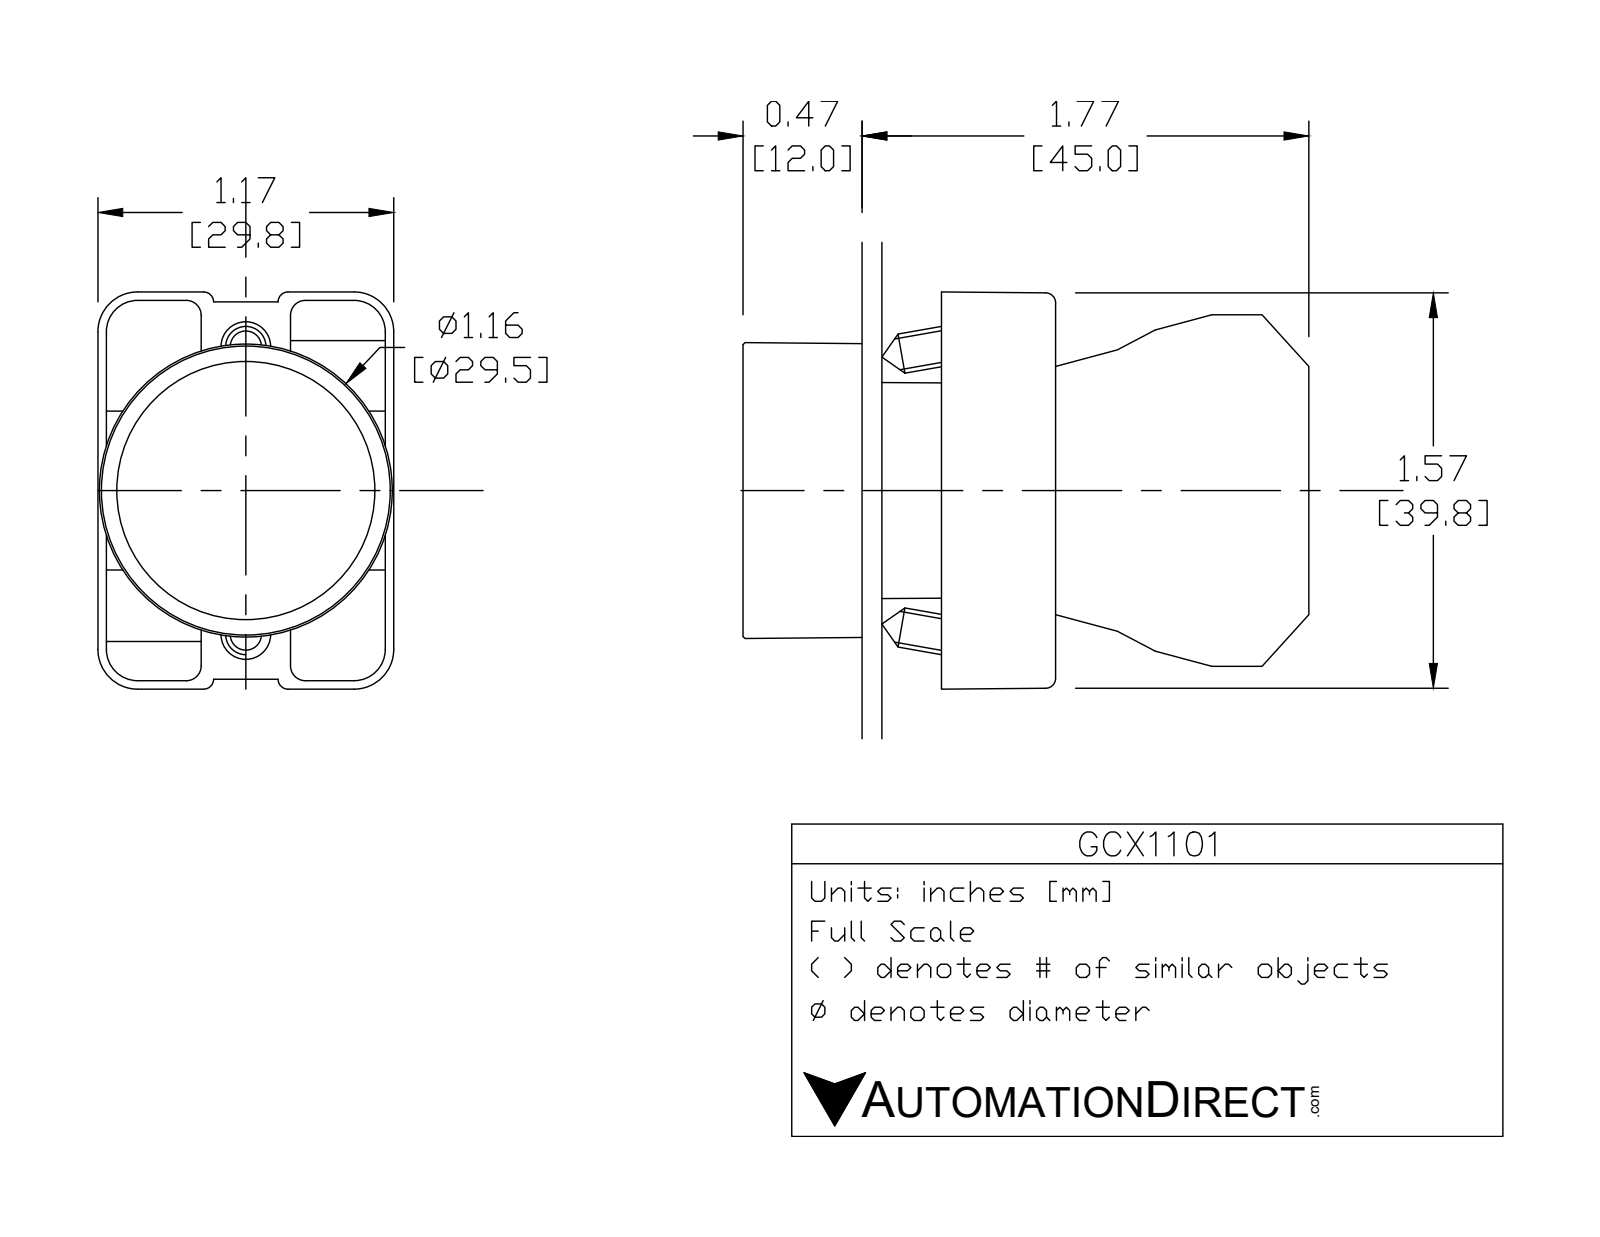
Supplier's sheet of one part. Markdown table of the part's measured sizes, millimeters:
| quantity | value |
| --- | --- |
| part name | ecx1040; ecx1029; GCX1101 OPERATOR; GCX1101 |
| STEP written by | SolidWorks 2016 (AUTOMOTIVE_DESIGN) |
| units | millimeters |
| bodies | 6 solids, 381 faces (222 planar, 132 cylindrical, 27 other) |
| overall size | 56.3 × 40.2 × 29.9 |
| volume | 28 530 mm³ |
| surface area | 17 510 mm² |
| round holes (diameter × count) | 2 × 2, 3.1 × 2, 3.3 × 2, 2.2 × 1, 5 × 1, 22.3 × 1, 22.6 × 1, 26 × 1 |
| round bosses / shafts (diameter × count) | 4 × 2, 29.8 × 1, 25.5 × 1, 24 × 1, 21.7 × 1, 19.8 × 1 |
| partial cylindrical surfaces (radius × count) | 1.5 × 24, 1 × 12, 3.1 × 12, 4 × 12, 1 × 4, 3.3 × 2, 0.5 × 1, 1.6 × 1 |
| main face-to-face distances | 18.3, 14.7, 0.8, 12, 30.3, 0.8, 17.5, 15.2, 29.5, 27.2 |
| hole center spacings | 6, 13.8, 12, 12.4 |
